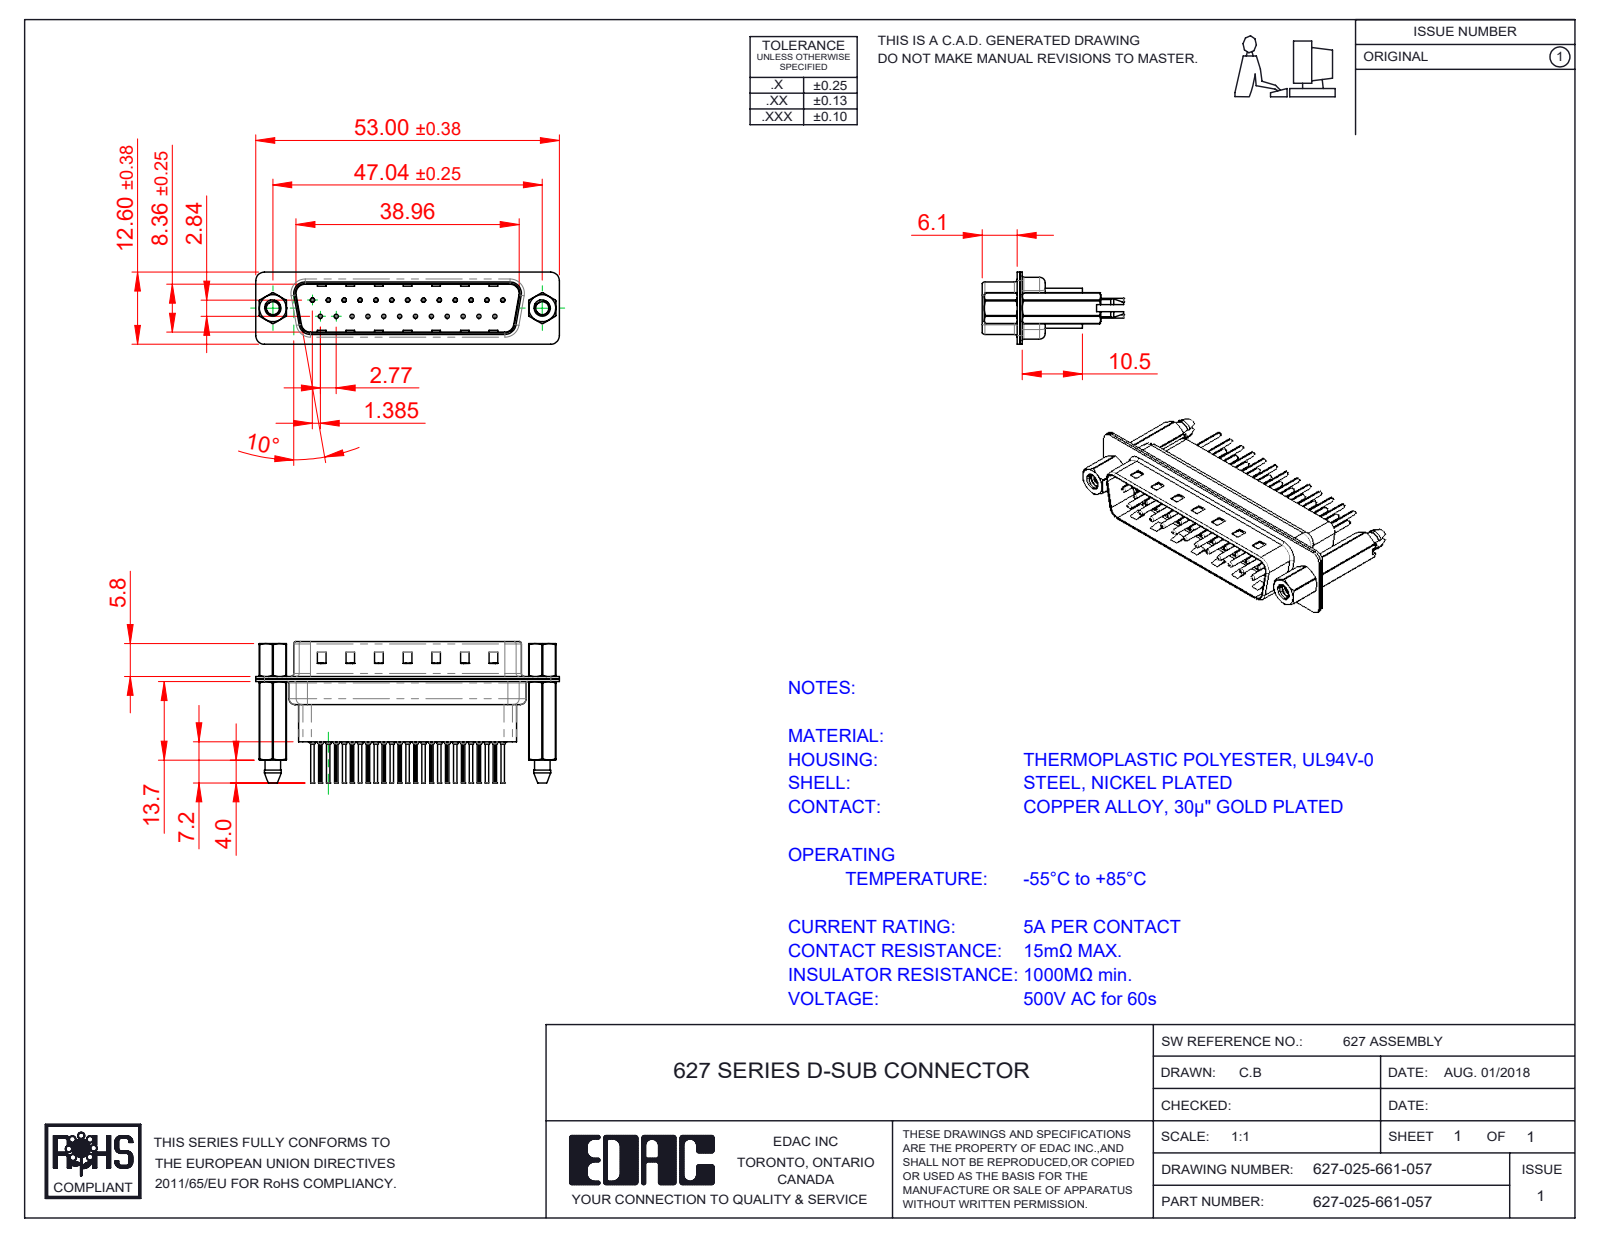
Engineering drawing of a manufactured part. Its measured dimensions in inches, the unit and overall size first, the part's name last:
Units: inches
Overall size (bounding box): 2.087 × 0.969 × 0.496
Round holes (diameter × count): ⌀0.008 ×25, ⌀0.014 ×25, ⌀0.043 ×25, ⌀0.063 ×25, ⌀0.089 ×2, ⌀0.09 ×2, ⌀0.157 ×2, ⌀0.189 ×2
Round bosses / shafts (diameter × count): ⌀0.079 ×25, ⌀0.059 ×25, ⌀0.03 ×25, ⌀0.024 ×25, ⌀0.193 ×2, ⌀0.11 ×2
Partial cylindrical surfaces — rounded edges, fillets, slot ends (radius × count): R0.004 ×50, R0.059 ×18, R0.079 ×12, R0.063 ×10, R0.02 ×8, R0.01 ×4, R0.024 ×4, R0.026 ×4
Main face-to-face distances: 0.016, 0.018, 0.032, 0.377, 0.027, 0.302, 0.059, 0.035, 0.043, 0.318
Hole centre spacings: 0.124, 0.327, 0.109, 0.218, 0.436, 0.654, 0.198, 0.198
Volume: 0.267 in³ · Surface area: 17.44 in²
Bodies: 32 solids, 3060 faces (825 planar, 1200 cylindrical, 1035 other)
Part name (STEP PRODUCT): 627 Contact Row 1_61; 627-025-661-057; 627 4-40 Hex Standoff; 627 Contact Row 2_61 (+4 more)
STEP written by: SolidWorks 2020 (CONFIG_CONTROL_DESIGN)
